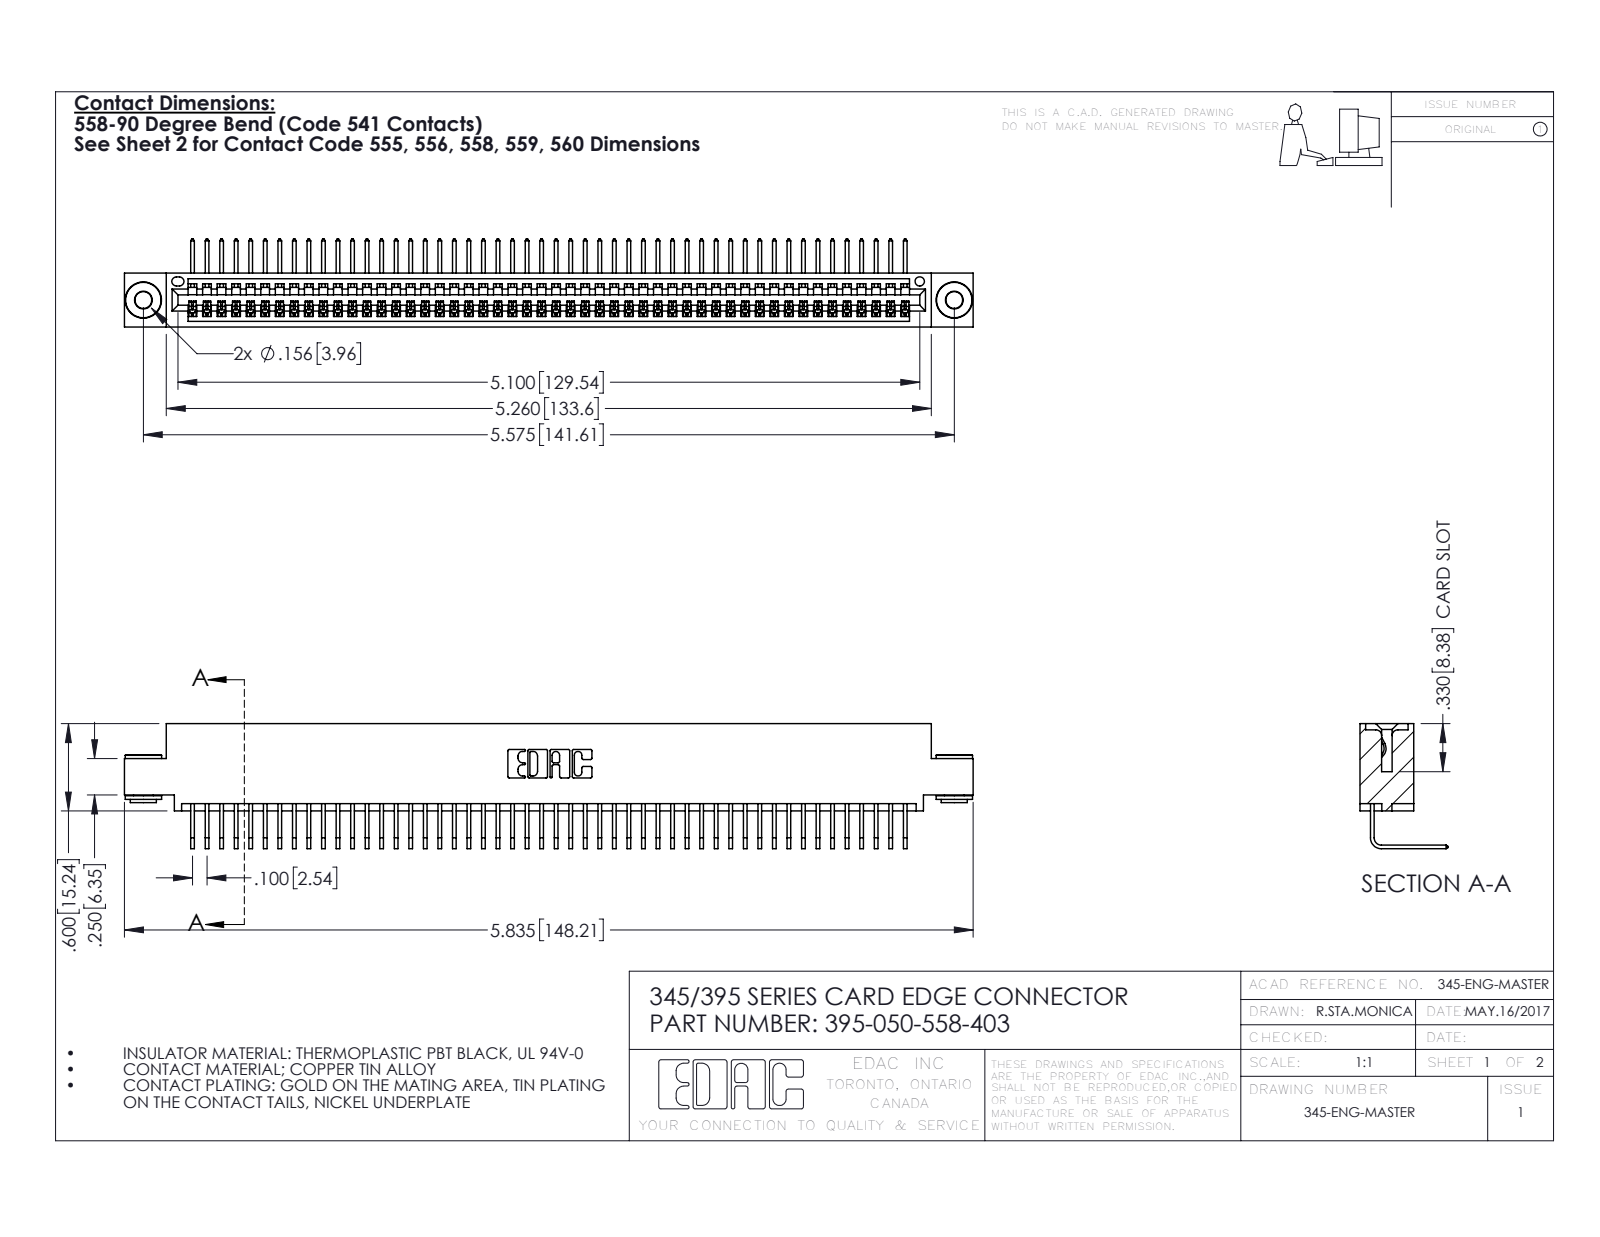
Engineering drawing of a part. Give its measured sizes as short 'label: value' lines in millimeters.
name: 345 Part_0.110 Offset - 0.156 Dia-TH; 395-050-558-403; 345-250-002_345-250-002-102; 345-292-001_558 Tail - 2
written by: SolidWorks 2016 (CONFIG_CONTROL_DESIGN)
unit: mm
bodies: 53 solids, 3168 faces (2194 planar, 966 cylindrical, 8 other)
size: 148.2 × 21.8 × 15.4
volume: 14 300 mm³; area: 20 330 mm²
holes: 2× ⌀2.9, 2× ⌀4, 1× ⌀1.6
bosses: 2× ⌀6.4, 2× ⌀4.6, 2× ⌀3.5
rounds: 100× R0.2, 22× R0.3, 6× R0.2, 6× R0.8, 3× R0.7, 2× R0.8, 2× R1, 1× R0.4
face distances: 1.8, 7.6, 9.4, 5.1, 0.6, 2.5, 6.9, 5.7, 3.8, 1.8
hole spacings: 6.9, 135.6, 141.6
